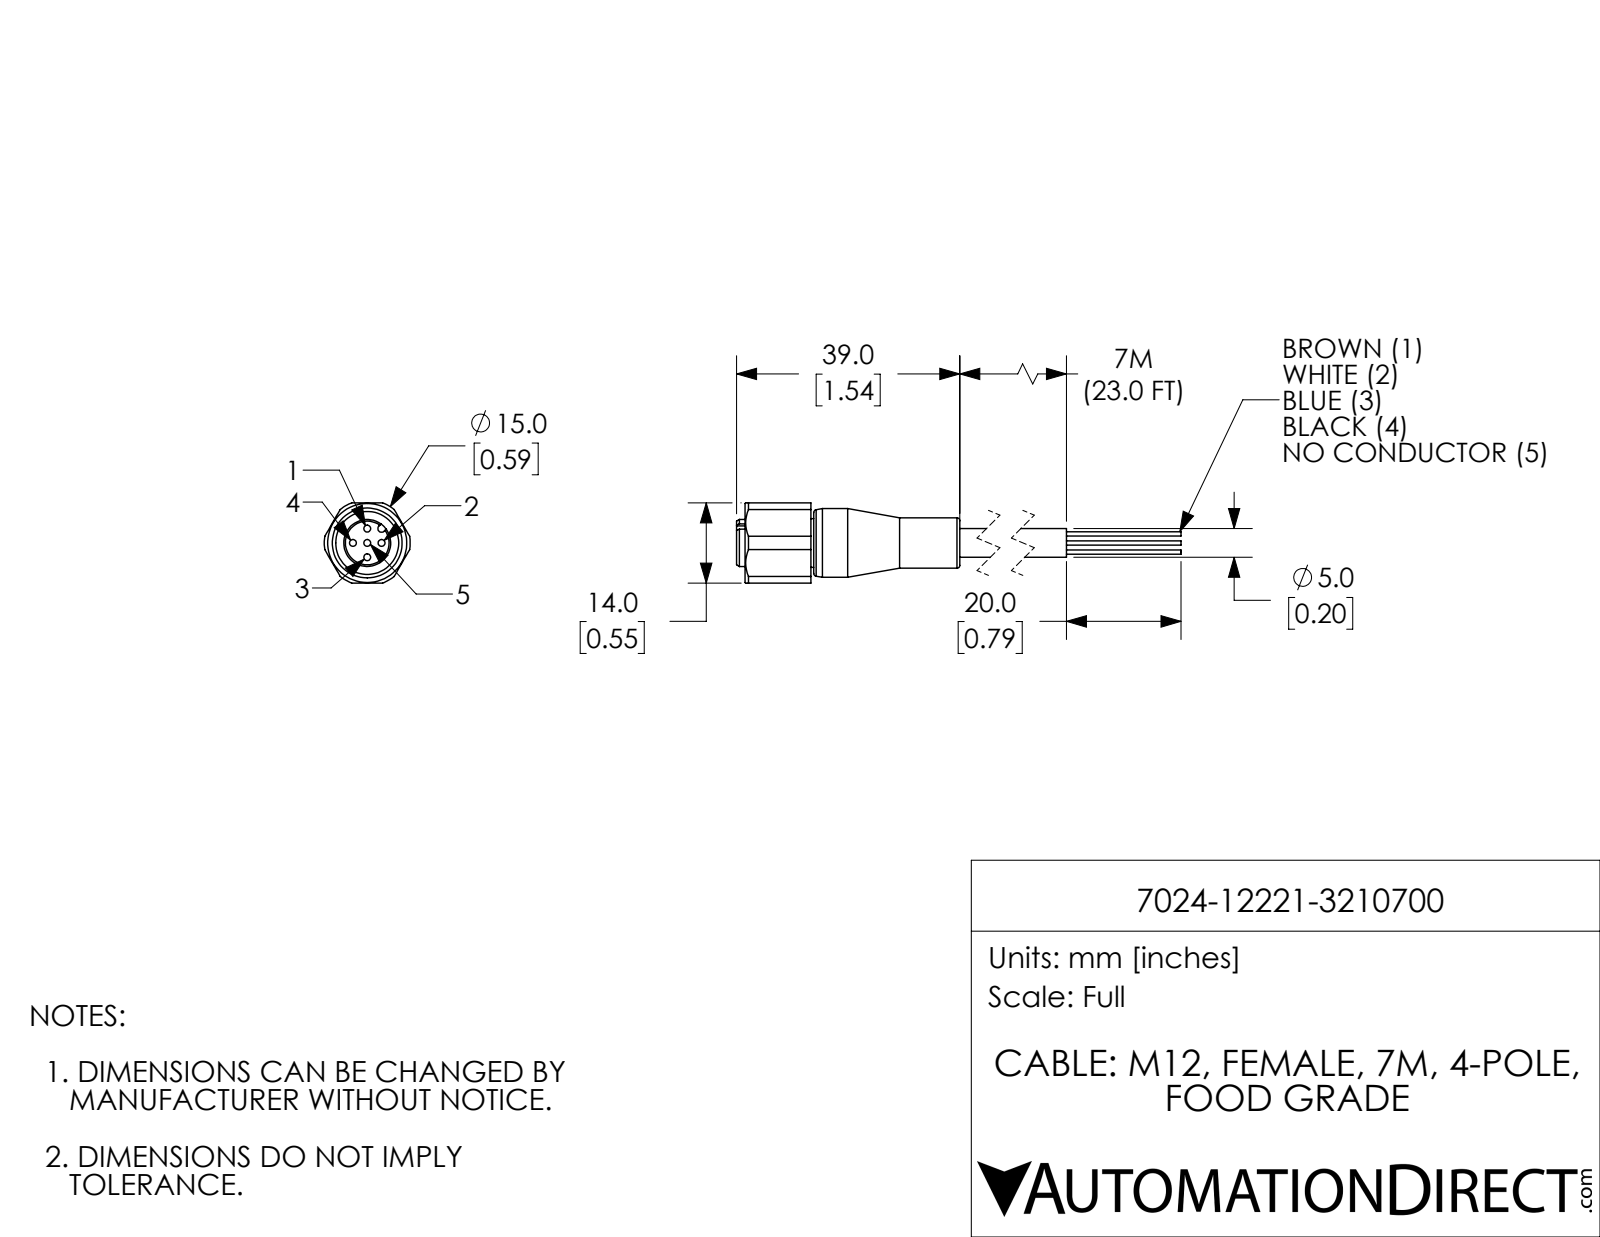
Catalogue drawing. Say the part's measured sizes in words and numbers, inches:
The part is named "7024-12221-3210700". Its 3-D file was written by "SolidWorks 2018 (AUTOMOTIVE_DESIGN)". It is 1 solid with 77 faces: 25 planar, 37 cylindrical and 15 other. Overall it measures 3.063 by 0.591 by 0.551 inches. Its volume is 0.251 cubic inches and its surface area 4.383 square inches. Round holes: 5 of diameter 0.047, 1 of diameter 0.433. Round bosses or shafts: 4 of diameter 0.03, 1 of diameter 0.472, 1 of diameter 0.346, 1 of diameter 0.335, 1 of diameter 0.323, 1 of diameter 0.197. Partial cylindrical surfaces (rounded edges, fillets, slot ends): 1 of radius 0.026, 1 of radius 0.295. The main face-to-face distances are 0.551, 0.157, 0.354, 0.512, 0.059, 0.295, 0.453, 0.531, 0.472, 0.177. The hole center spacings are 0.098, 0.139, 0.197.
